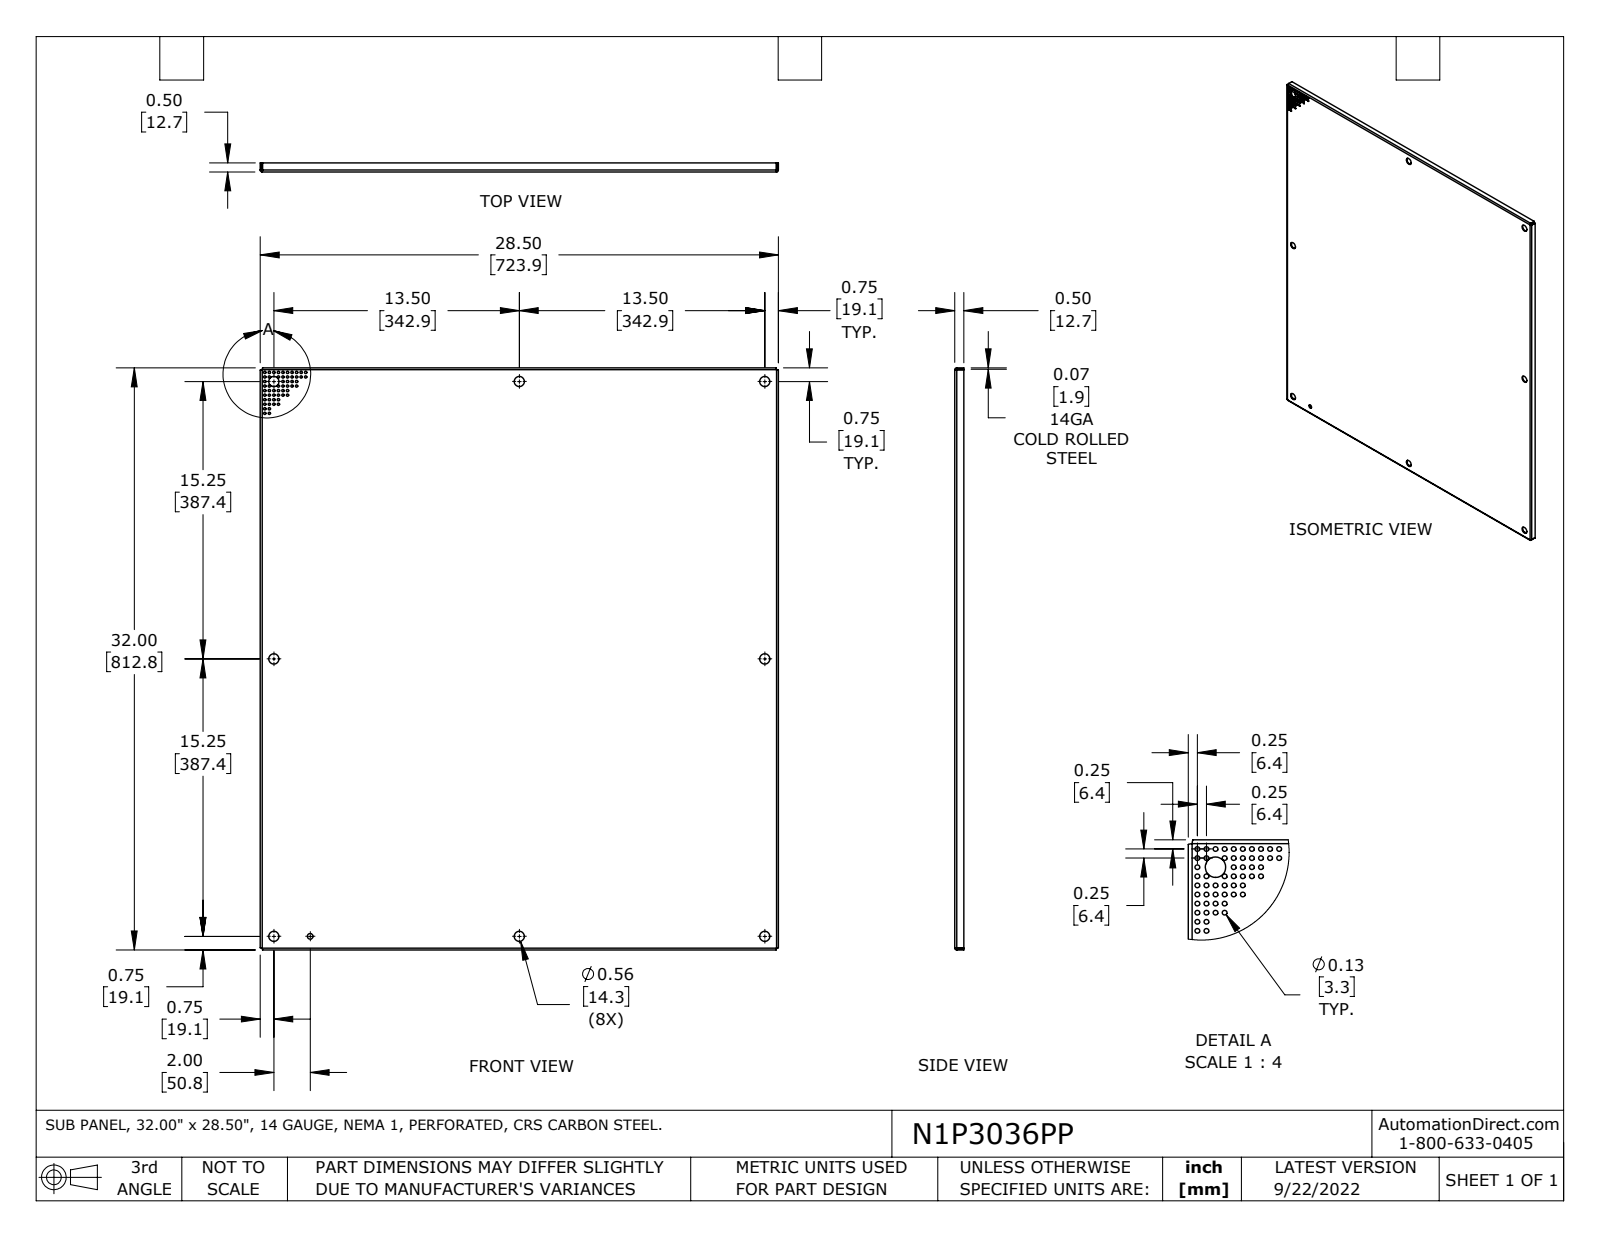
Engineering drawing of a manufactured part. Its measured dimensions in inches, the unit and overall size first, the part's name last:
Units: inches
Overall size (bounding box): 32 × 28.5 × 0.5
Round holes (diameter × count): ⌀0.13 ×55, ⌀0.563 ×8, ⌀0.312 ×1
Partial cylindrical surfaces — rounded edges, fillets, slot ends (radius × count): R0.031 ×4, R0.105 ×4
Main face-to-face distances: 0.074, 28.426, 31.926, 28.5, 28.352, 32, 31.852, 0.426, 0.5, 0.126
Hole centre spacings: 0.25, 0.559, 1.25, 0.791, 0.5, 1.031, 0.354, 0.902
Volume: 70.8 in³ · Surface area: 1 925 in²
Bodies: 1 solid, 166 faces (22 planar, 136 cylindrical, 8 other)
Part name (STEP PRODUCT): N1P3036PP
STEP written by: SolidWorks 2021 (AUTOMOTIVE_DESIGN)
